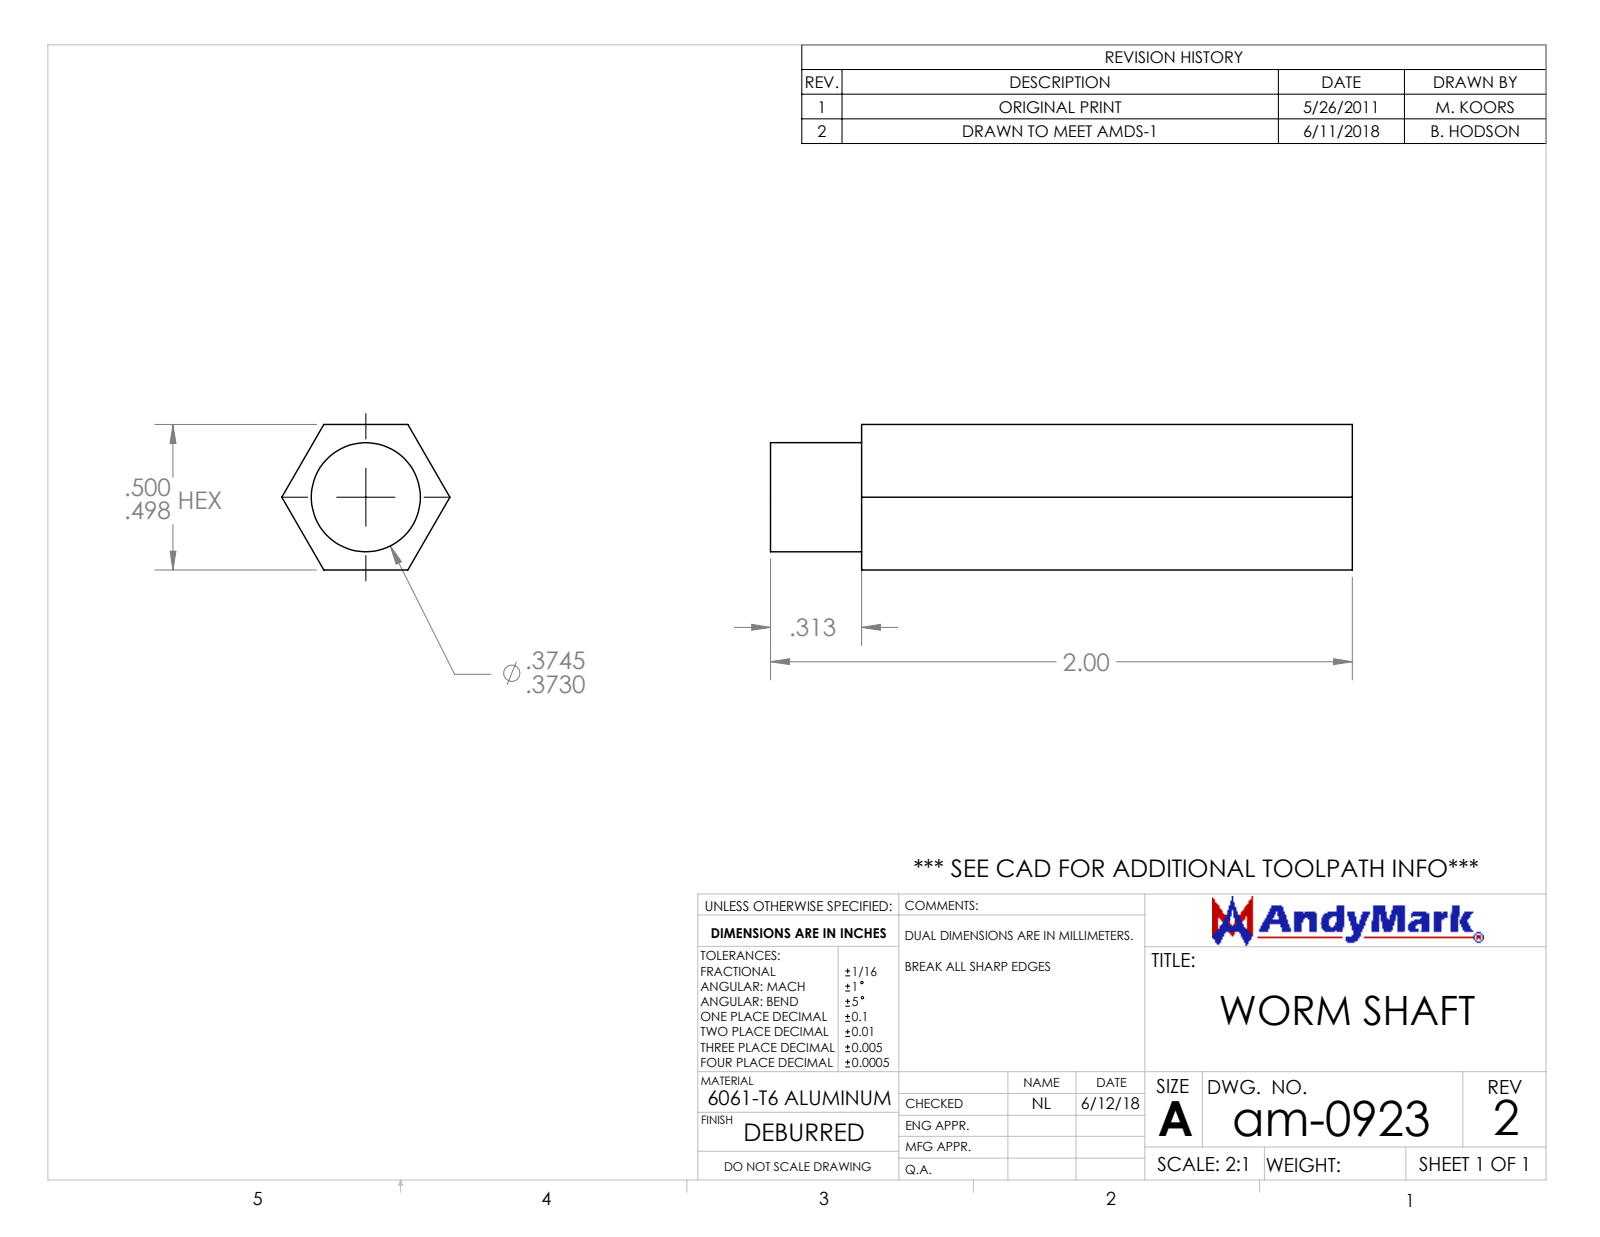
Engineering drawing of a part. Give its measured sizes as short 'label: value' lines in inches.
name: am-0923 Worm Shaft for Worm Gearbox REV2
written by: SolidWorks 2017 (AUTOMOTIVE_DESIGN)
unit: in
bodies: 1 solid, 11 faces (9 planar, 2 cylindrical, 0 other)
size: 2 × 0.577 × 0.5
volume: 0.4 in³; area: 3.724 in²
bosses: 1× ⌀0.375
face distances: 0.5, 2, 1.687, 0.313
